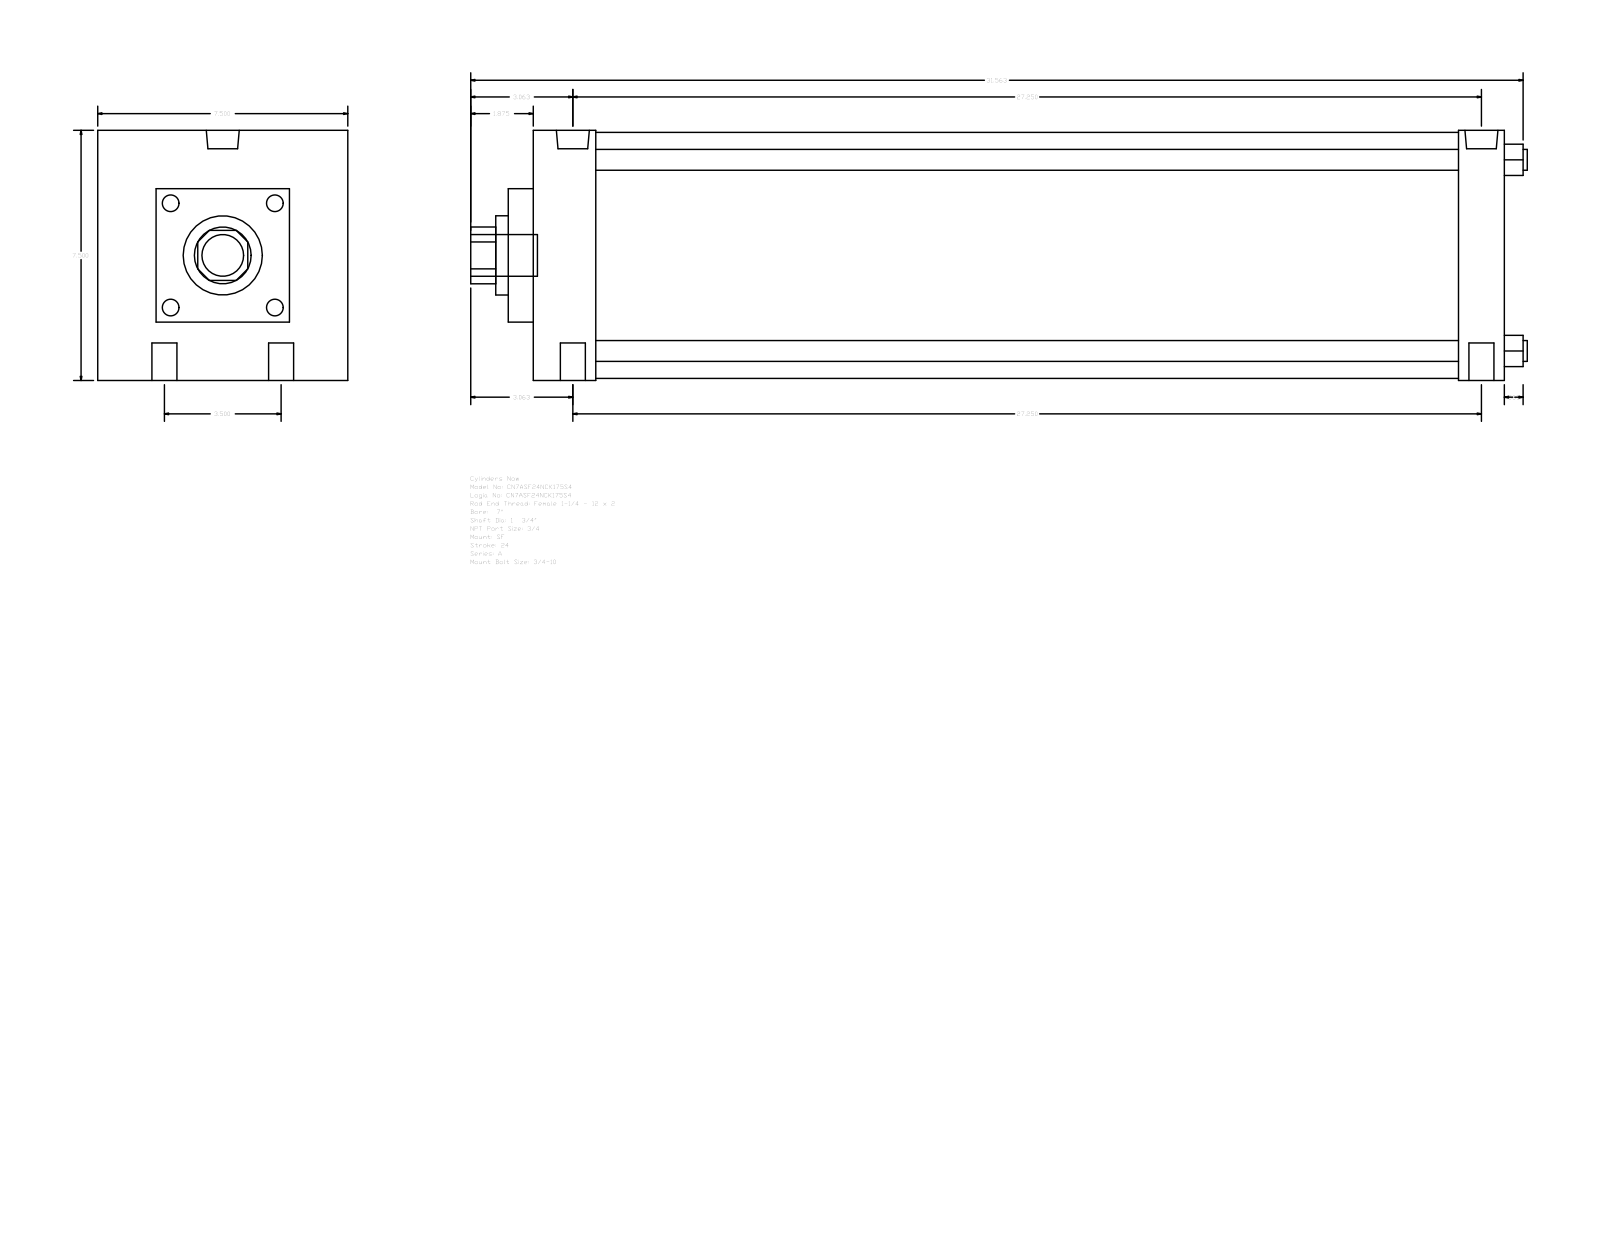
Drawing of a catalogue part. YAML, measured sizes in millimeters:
part_name: "A_SF__0700_1.75"
step_written_by: "GSSL Pune (CONFIG_CONTROL_DESIGN)"
units: millimeters
bodies: {solids: 0, faces: 93, planar: 67, cylindrical: 26, other: 0}
overall_size: [804.86, 190.5, 190.5]
round_holes:
  - {diameter: 19.05, count: 4}
  - {diameter: 15.08, count: 2}
  - {diameter: 25.12, count: 2}
  - {diameter: 44.45, count: 1}
  - {diameter: 60.33, count: 1}
round_bosses_or_shafts:
  - {diameter: 15.88, count: 4}
  - {diameter: 187.32, count: 1}
  - {diameter: 31.75, count: 1}
partial_cylinders:
  - {radius: 21.63, count: 1}
face_to_face_distances: [190.5, 739.78, 44.45, 34.92, 19.05, 47.63, 704.86, 657.23, 692.15, 146.05]
hole_center_spacings: [44.45, 693.58, 692.15, 88.9, 697.84, 681.03]
